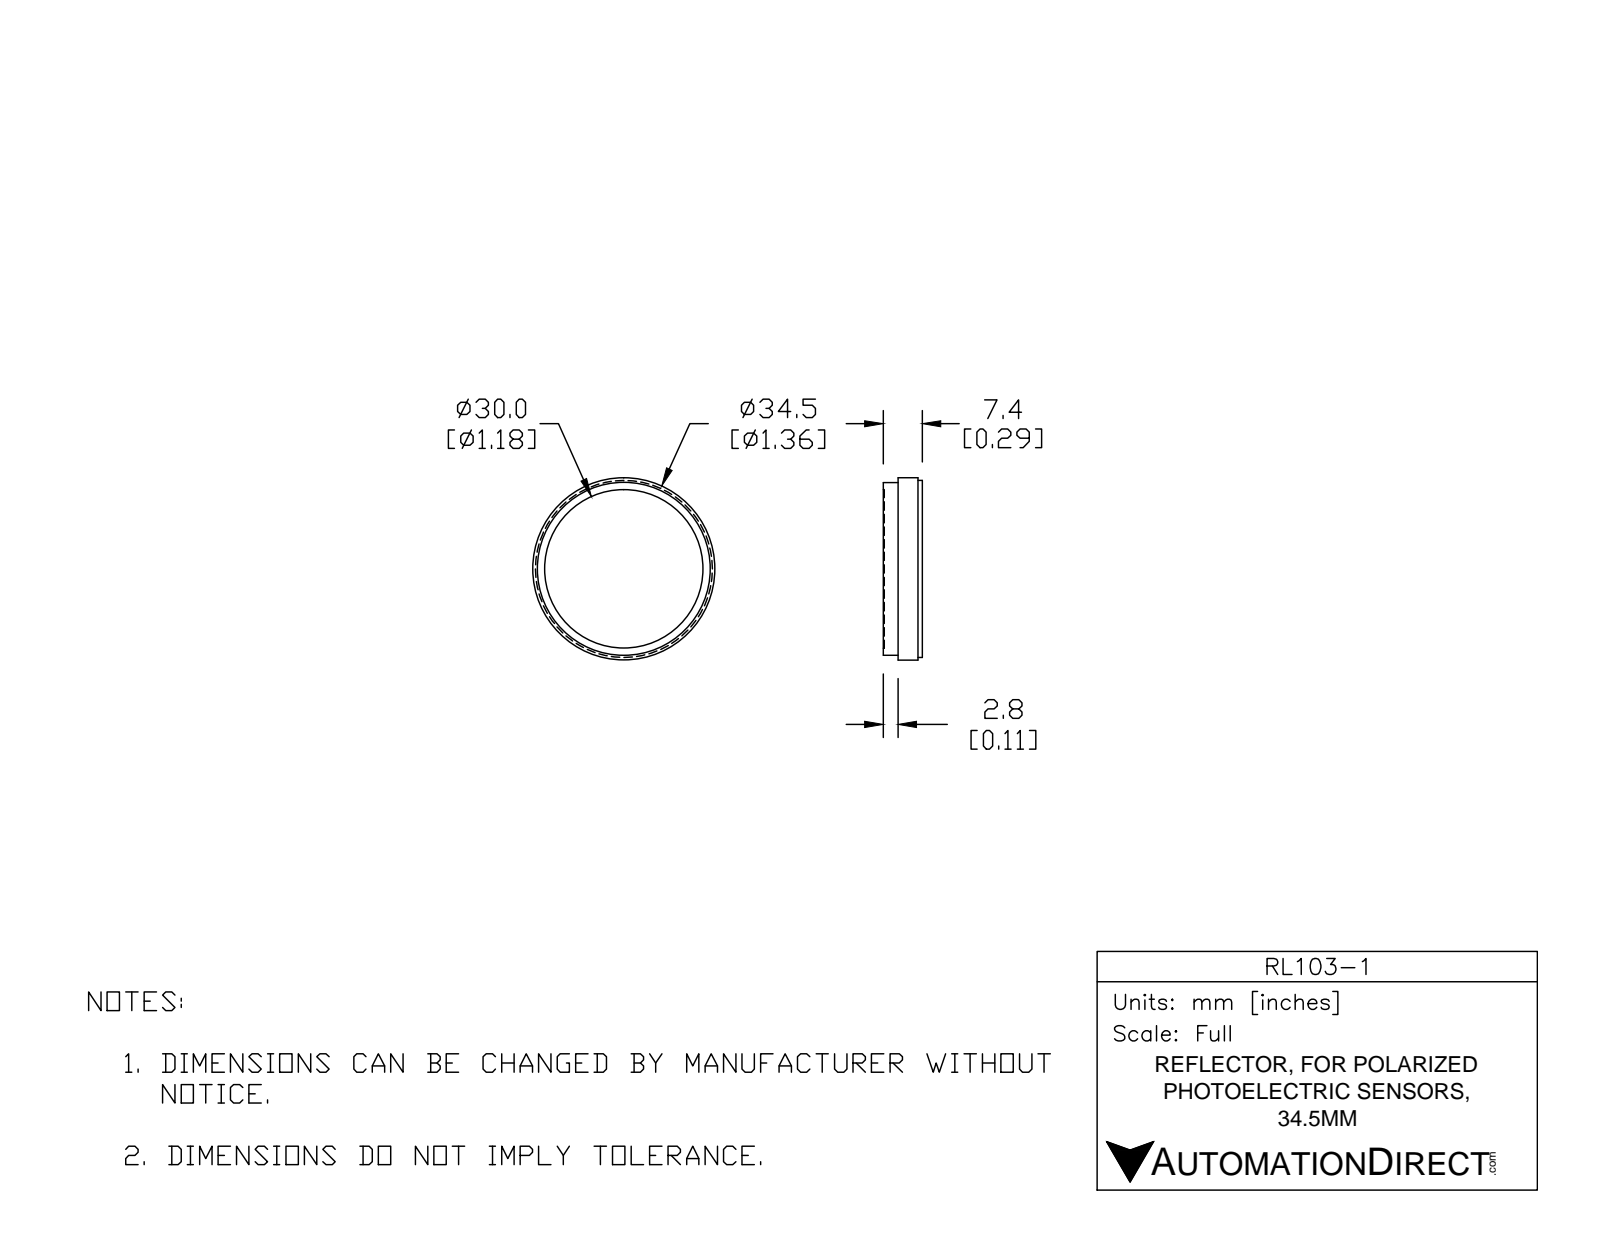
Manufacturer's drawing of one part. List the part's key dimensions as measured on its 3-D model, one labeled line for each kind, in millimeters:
Part name (STEP PRODUCT): RL-103-1
STEP written by: SolidWorks 2017 (AUTOMOTIVE_DESIGN)
Units: millimetres
Bodies: 1 solid, 13 faces (5 planar, 8 cylindrical, 0 other)
Overall size (bounding box): 34.5 × 34.5 × 7.4
Volume: 6 470 mm³ · Surface area: 2 672 mm²
Round holes (diameter × count): ⌀30 ×1
Round bosses / shafts (diameter × count): ⌀34.5 ×1, ⌀33.5 ×1, ⌀32.7 ×1
Main face-to-face distances: 7.2, 7.4, 4.6, 2.6, 2.8, 0.8, 3.8, 6.4, 6.6
